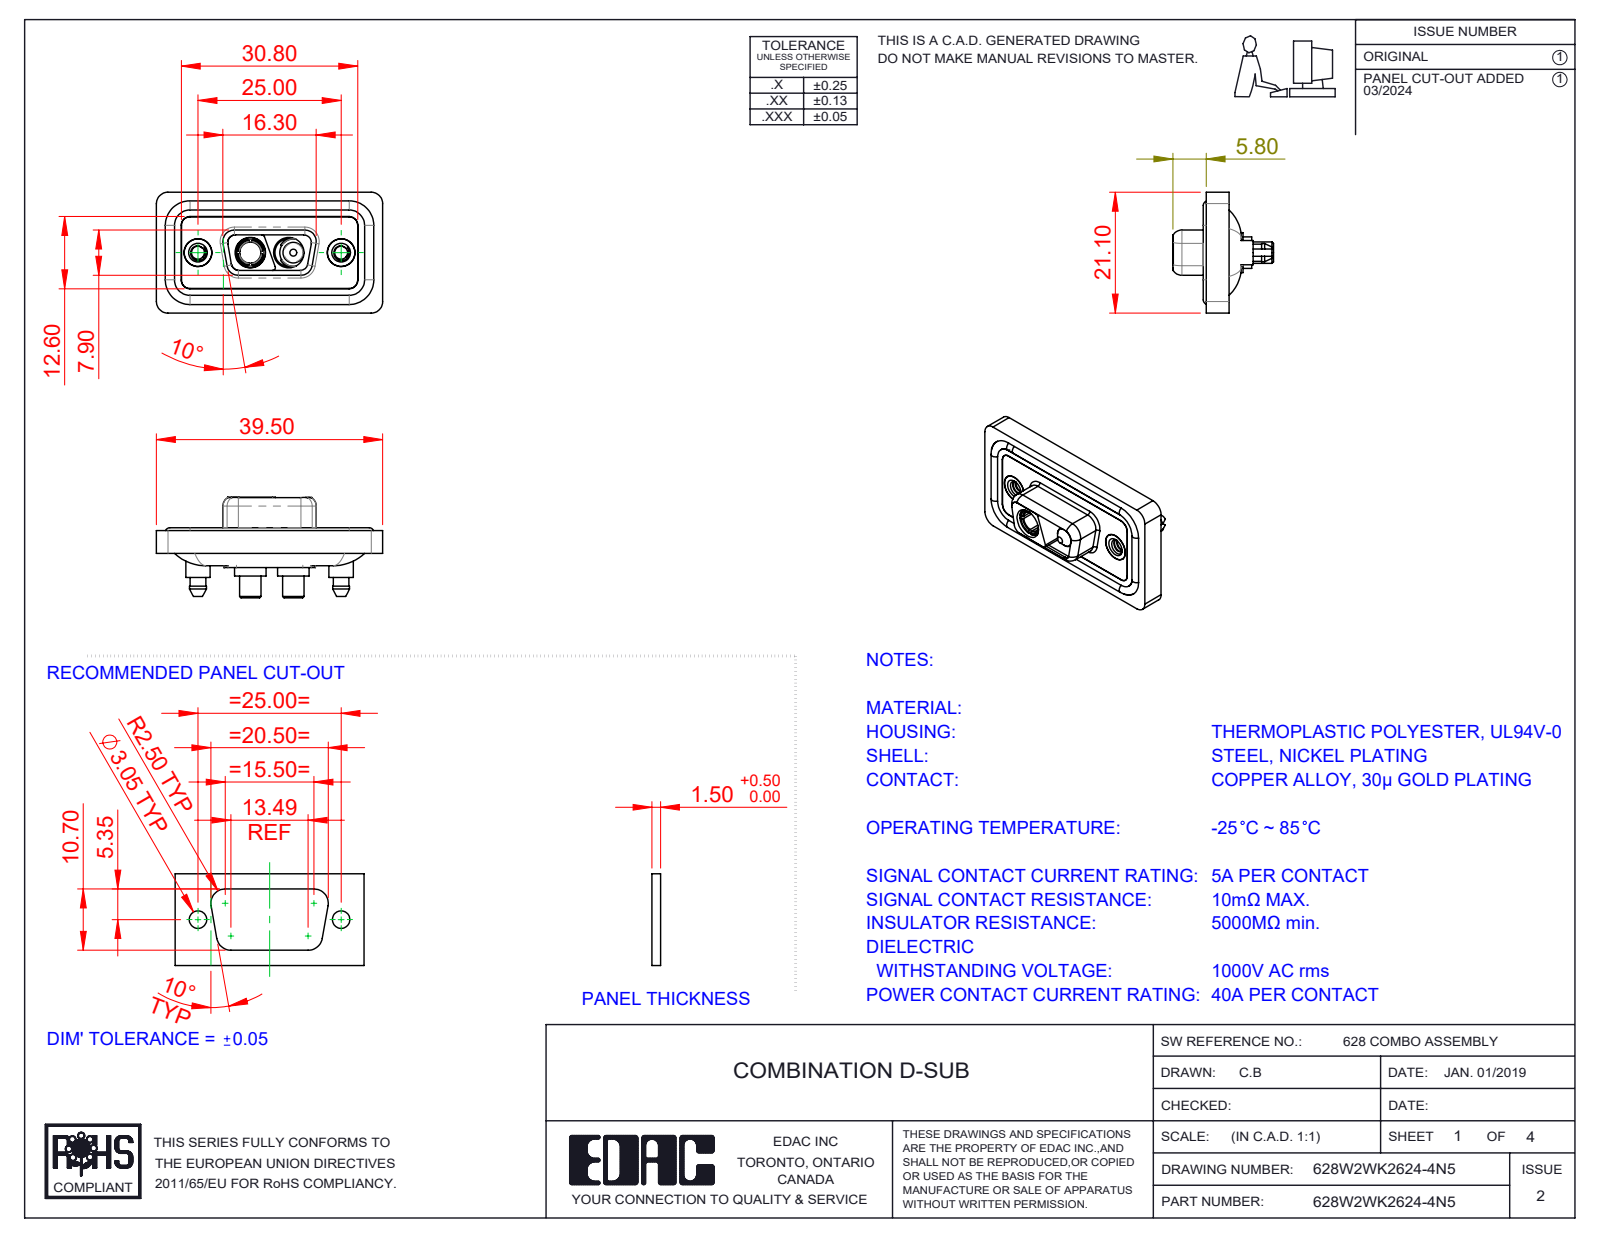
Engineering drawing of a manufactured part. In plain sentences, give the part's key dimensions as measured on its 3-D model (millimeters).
The part is named "Power Pin_40A S; Power Socket_40A S; 628Combo Shell Rear_09 Contacts; 628Combo Housing_2WK2 (+4 more)". Its 3-D file was written by "SolidWorks 2023 (CONFIG_CONTROL_DESIGN)". It is 11 solids with 550 faces: 160 planar, 263 cylindrical and 127 other. Overall it measures 39.5 by 21.1 by 17.55 millimeters. Its volume is 4 774 cubic millimeters and its surface area 7 698 square millimeters. Round holes: 4 of diameter 4.85, 2 of diameter 2.26, 2 of diameter 4, 2 of diameter 4.05, 2 of diameter 5, 2 of diameter 5.3, 1 of diameter 3.7. Round bosses or shafts: 4 of diameter 1.6, 2 of diameter 5.5, 2 of diameter 5.4, 2 of diameter 5.2, 2 of diameter 4.95, 2 of diameter 4.8, 2 of diameter 4.75, 2 of diameter 4.25. Partial cylindrical surfaces (rounded edges, fillets, slot ends): 24 of radius 1.5, 18 of radius 2, 10 of radius 1.6, 8 of radius 1.35, 6 of radius 0.5, 4 of radius 0.25, 4 of radius 0.6, 4 of radius 0.65. The main face-to-face distances are 0.4, 1.1, 2.9, 1.6, 0.5, 1.8, 5.65, 4, 1.5, 5.35. The hole center spacings are 9.14, 15.86, 6.72, 25.
